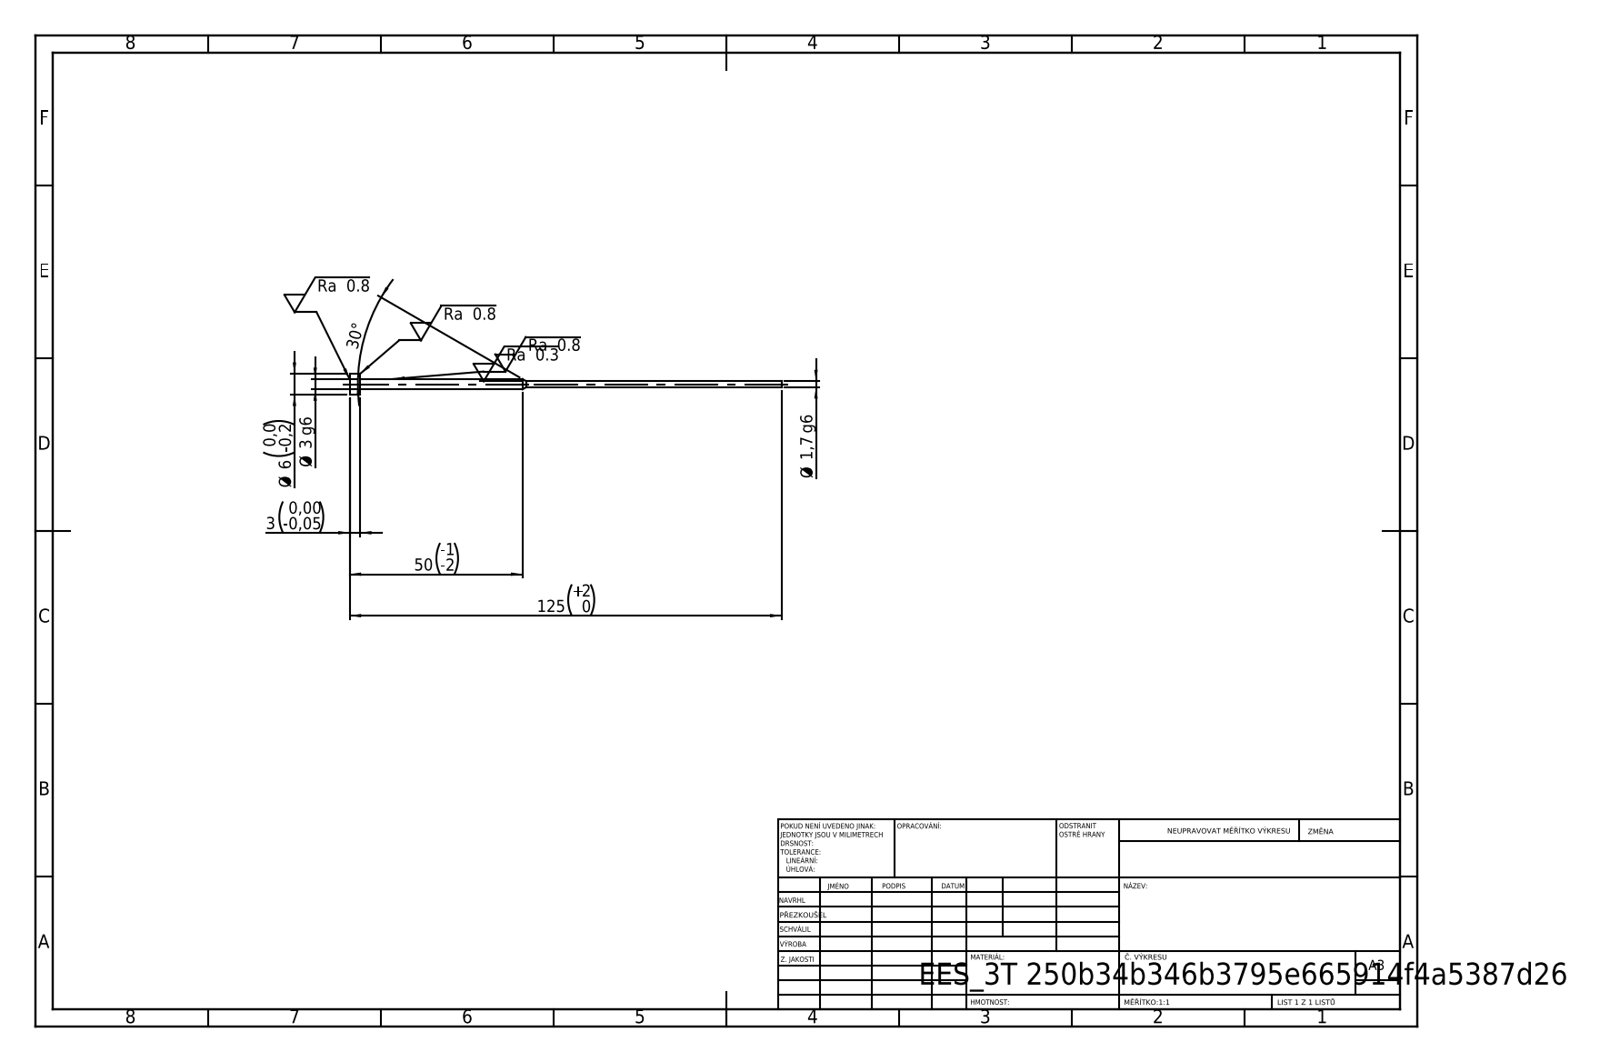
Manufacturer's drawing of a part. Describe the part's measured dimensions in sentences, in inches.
Its 3-D file was written by "SolidWorks 2019 (CONFIG_CONTROL_DESIGN)". It is 1 solid with 11 faces: 3 planar, 6 cylindrical and 2 other. Overall it measures 4.921 by 0.236 by 0.236 inches. Its volume is 0.036 cubic inches and its surface area 1.48 square inches. Round bosses or shafts: 1 of diameter 0.236, 1 of diameter 0.118, 1 of diameter 0.067. The main face-to-face distances are 0.118, 4.803, 4.921.
